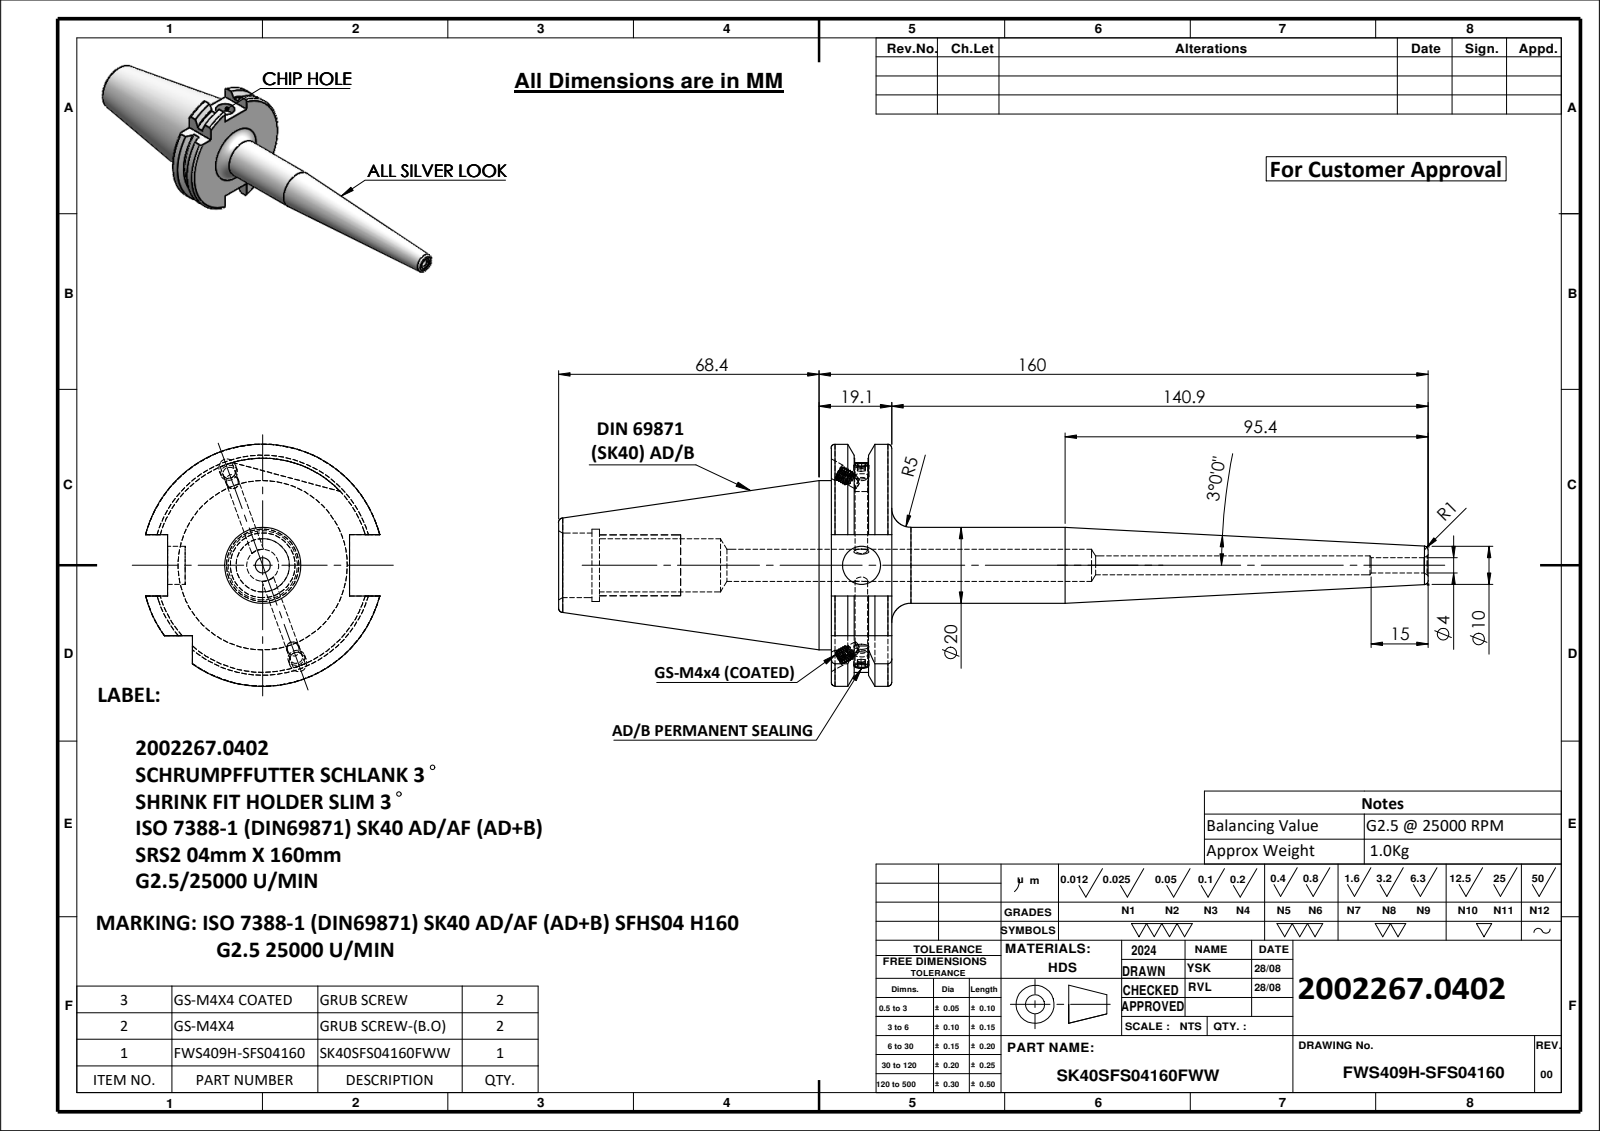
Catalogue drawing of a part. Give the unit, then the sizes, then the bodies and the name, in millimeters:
Units: millimetres
Overall size (bounding box): 228.4 × 63.55 × 61.48
Round holes (diameter × count): ⌀3.3 ×3, ⌀4.5 ×2, ⌀4 ×1, ⌀5 ×1, ⌀8.4 ×1, ⌀10 ×1, ⌀14 ×1, ⌀17 ×1, ⌀19 ×1
Round bosses / shafts (diameter × count): ⌀4 ×4, ⌀2.9 ×2, ⌀44.45 ×1, ⌀20 ×1
Partial cylindrical surfaces — rounded edges, fillets, slot ends (radius × count): R28.12 ×1, R31.77 ×1
Main face-to-face distances: 15.9, 16.1, 47.8, 71.6, 87.5, 10.7, 60.9, 76.8, 77.63, 66.93
Volume: 130 348 mm³ · Surface area: 30 818 mm²
Bodies: 5 solids, 244 faces (62 planar, 70 cylindrical, 112 other)
Part name (STEP PRODUCT): FWS409H-SFS04160; GS-M4X4_DIN 913 - M4 x 4-N; SK40SFS04160FWW; GS-M4X4-COATING_DIN 913 - M4 x 4-N
STEP written by: SolidWorks 2024 (CONFIG_CONTROL_DESIGN)
